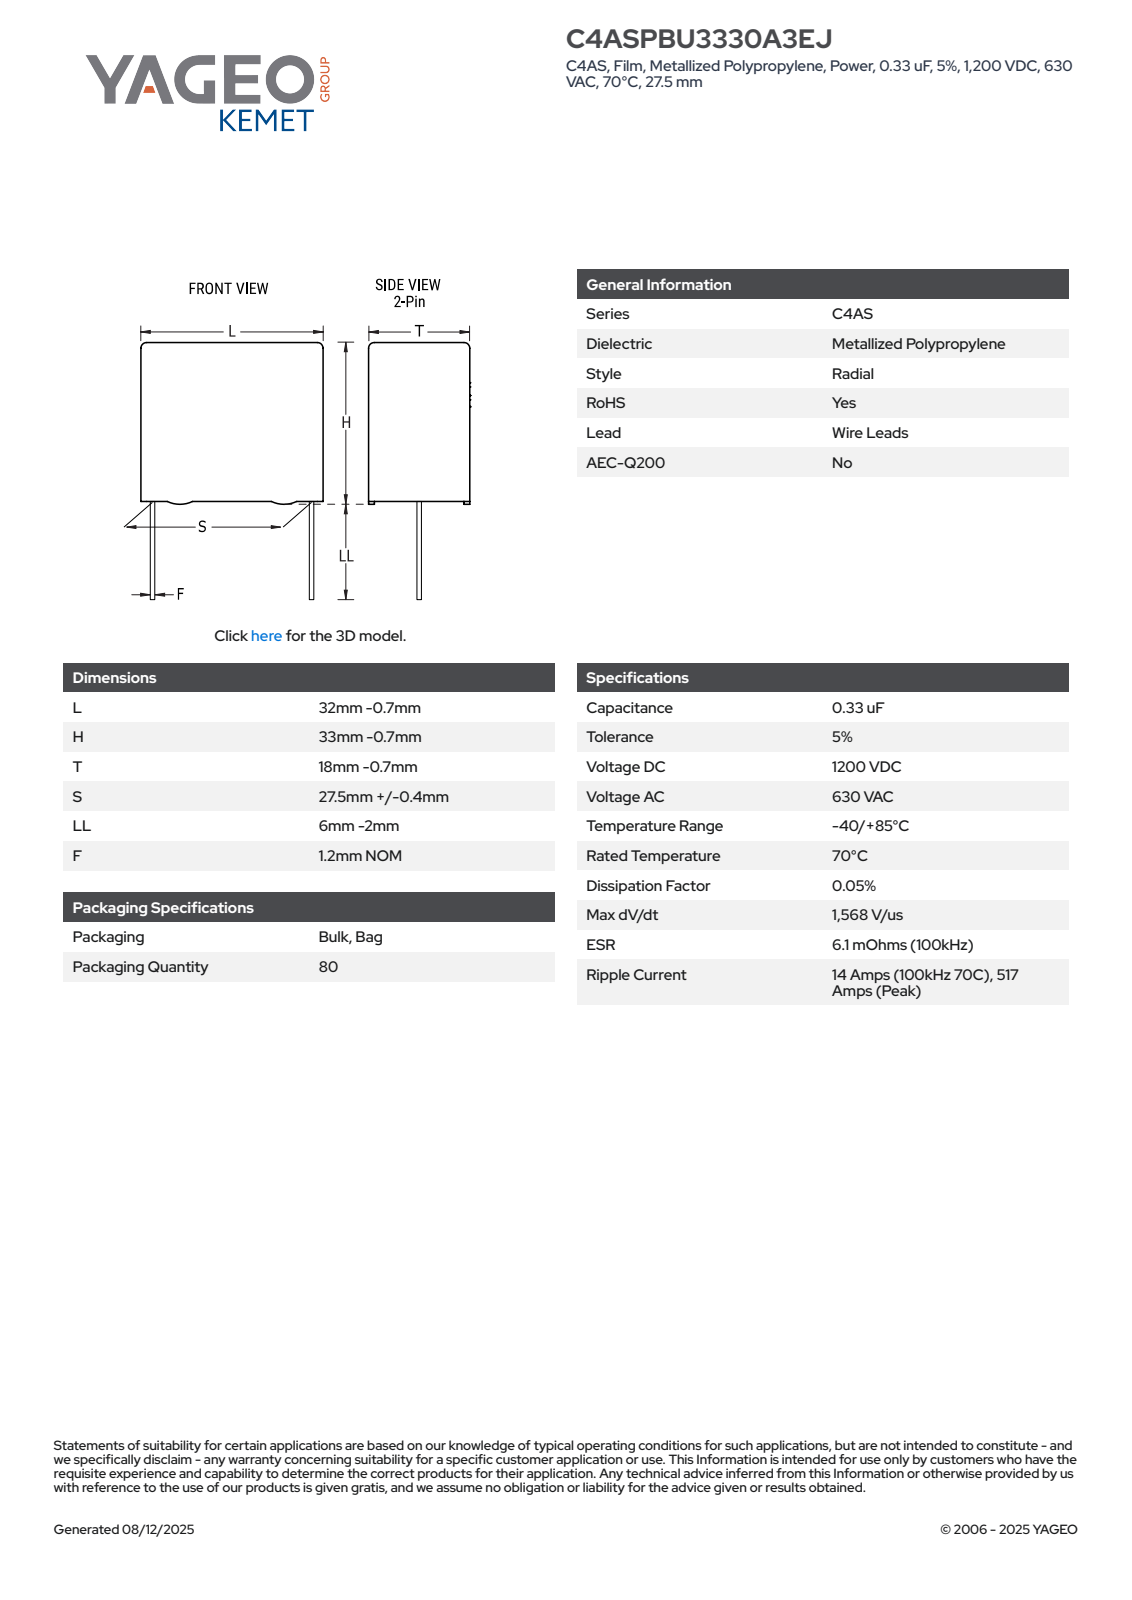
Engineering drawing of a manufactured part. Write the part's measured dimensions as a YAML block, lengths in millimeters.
part_name: "CFP_RB_32X33X18_L31.3H32.3T17.3S27.5LL4F1.2"
step_written_by: "SolidWorks 2014 (AUTOMOTIVE_DESIGN)"
units: millimeters
bodies: {solids: 4, faces: 89, planar: 81, cylindrical: 8, other: 0}
overall_size: [36.3, 31.3, 17.3]
volume: 17157
surface_area: 4246
round_bosses_or_shafts:
  - {diameter: 1.2, count: 2}
partial_cylinders:
  - {radius: 0.5, count: 4}
face_to_face_distances: [17.3, 31.3, 31.65, 0.65, 32.3, 0.99, 16.31, 15.32, 20.67, 4]
